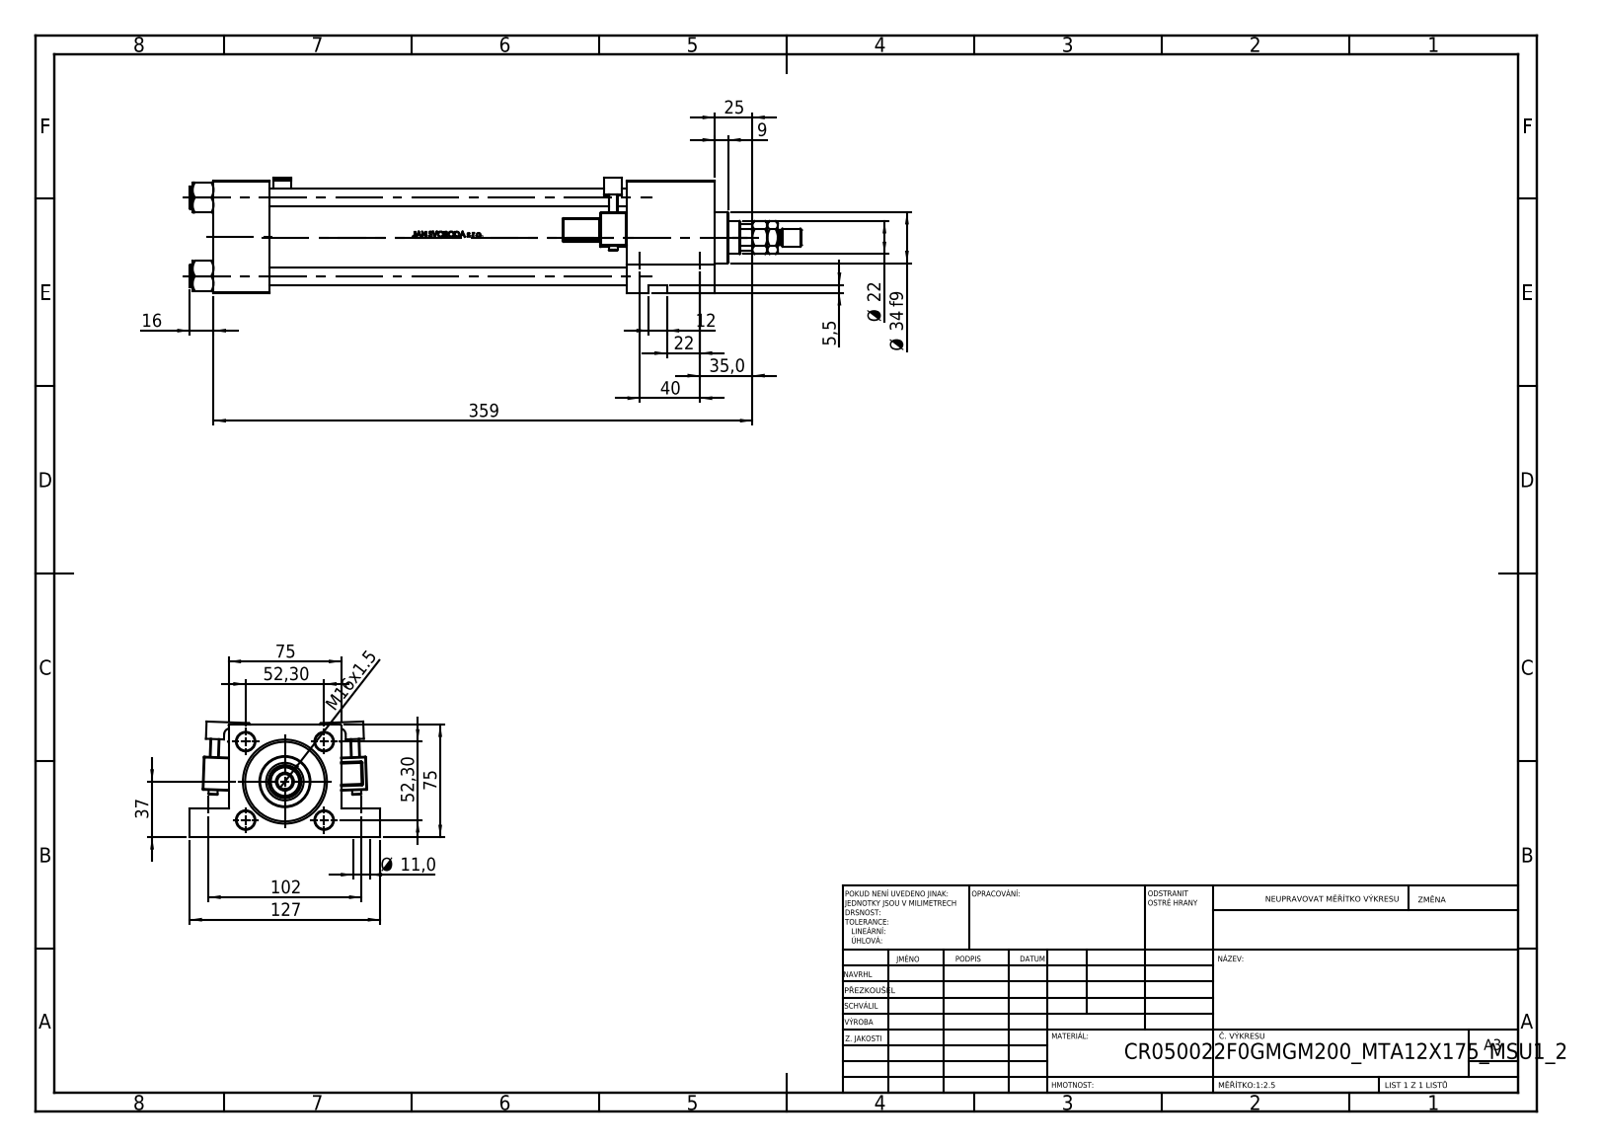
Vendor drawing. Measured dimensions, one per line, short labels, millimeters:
name: V215CR_MSU; NUT_M5_F; V215CR_F_Body; MTA (+3 more)
written by: SolidWorks 2019 (CONFIG_CONTROL_DESIGN)
unit: mm
bodies: 14 solids, 1306 faces (510 planar, 190 cylindrical, 606 other)
size: 408 × 127 × 77.03
volume: 994 590 mm³; area: 270 463 mm²
holes: 4× ⌀11, 4× ⌀12, 2× ⌀7, 2× ⌀30, 1× ⌀10.5, 1× ⌀17, 1× ⌀20.96, 1× ⌀22, 1× ⌀25, 1× ⌀41, 1× ⌀50, 1× ⌀53
bosses: 4× ⌀15, 2× ⌀6, 1× ⌀56, 1× ⌀34, 1× ⌀12, 1× ⌀10
rounds: 48× R0.5, 2× R1, 2× R2.5, 2× R4, 1× R10.5
face distances: 75, 37, 334, 297, 275, 238, 59, 19, 56, 305.3
hole spacings: 52.3, 36.63, 37.34, 40, 73.96, 102, 109.56, 273.5
